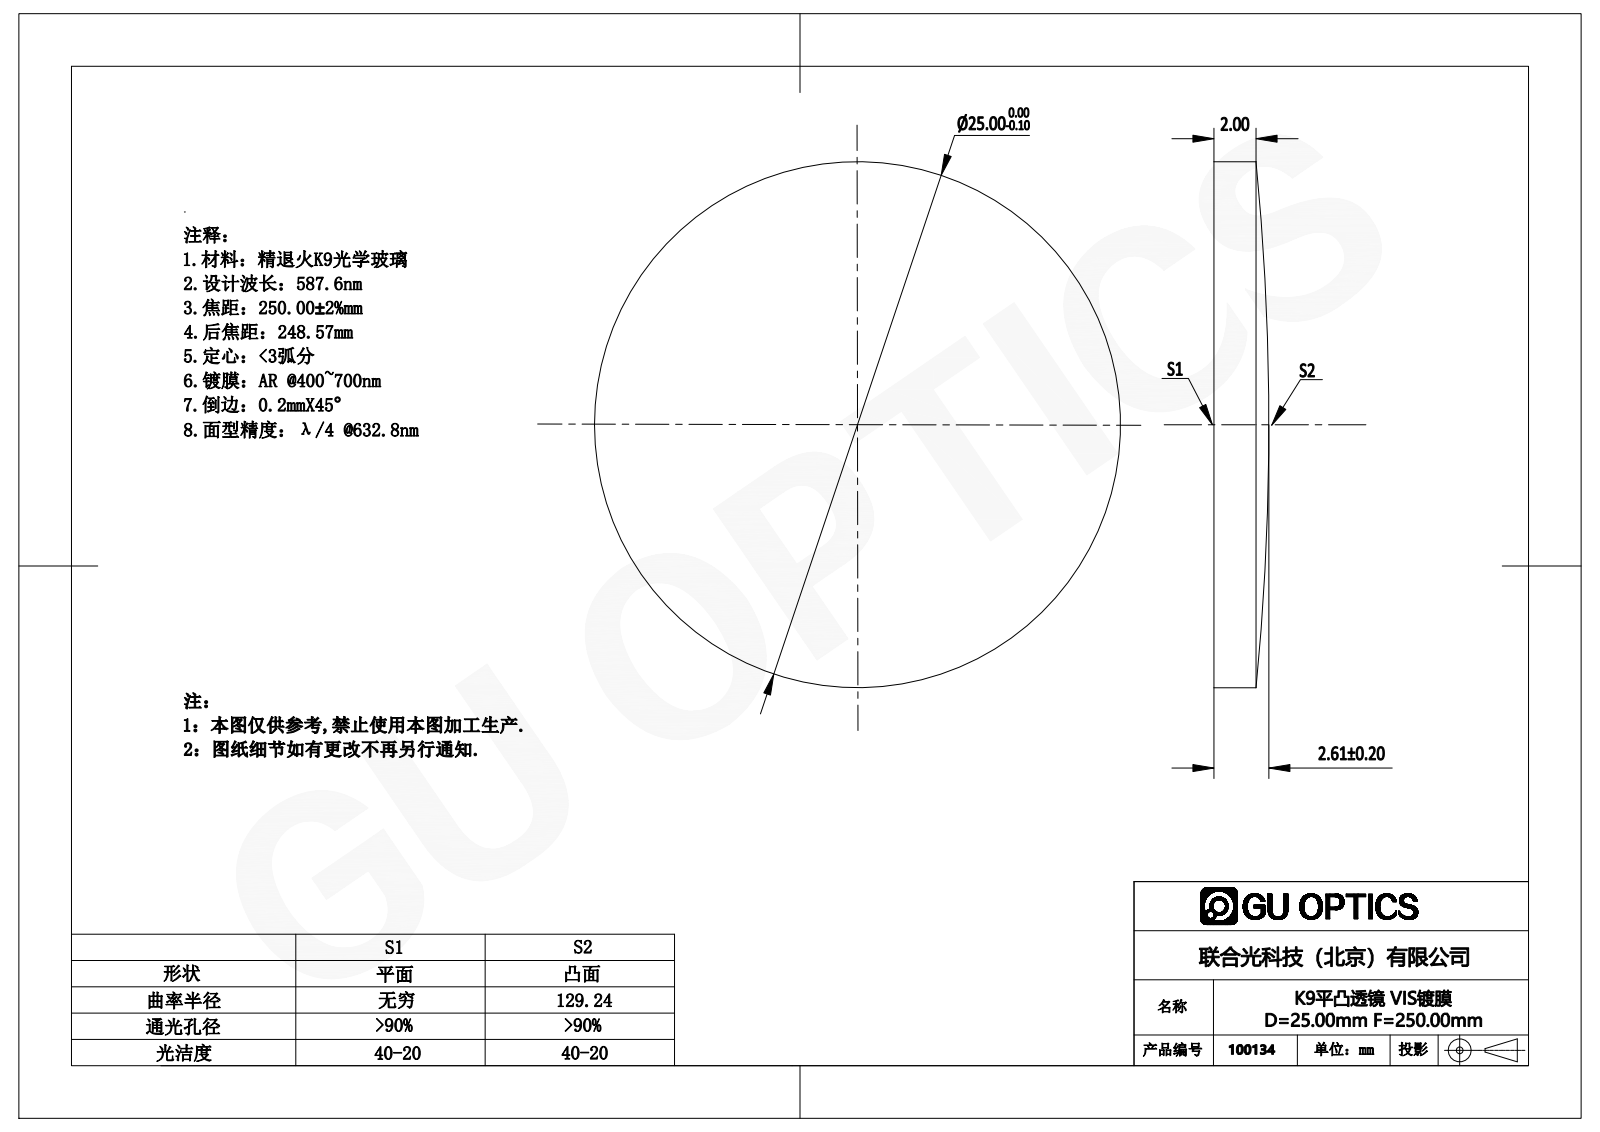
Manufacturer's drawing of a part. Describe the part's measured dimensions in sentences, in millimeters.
The part is named "100134". Its 3-D file was written by "SolidWorks 2016 (AUTOMOTIVE_DESIGN)". It is 1 solid with 5 faces: 1 planar, 2 cylindrical and 2 other. Overall it measures 25 by 25 by 2.61 millimeters. Its volume is 1 132 cubic millimeters and its surface area 1 140 square millimeters. Round bosses or shafts: 1 of diameter 25.
